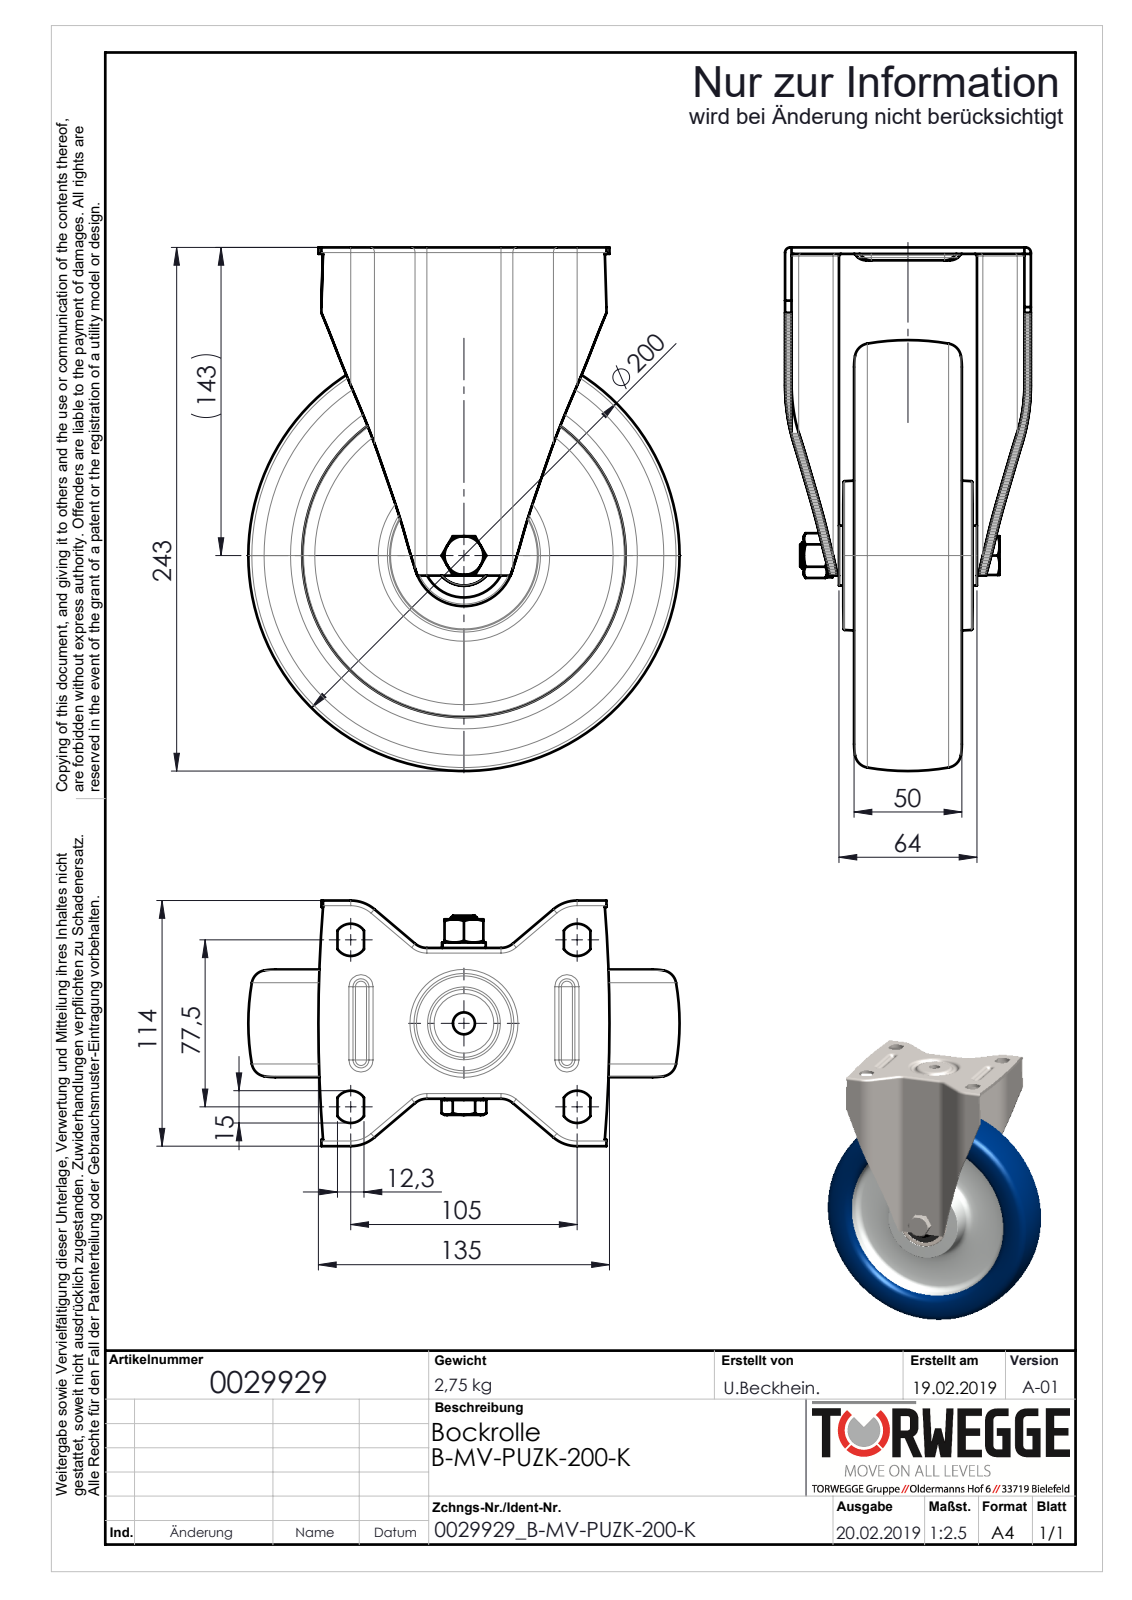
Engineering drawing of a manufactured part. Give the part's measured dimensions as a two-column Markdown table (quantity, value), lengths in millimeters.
| quantity | value |
| --- | --- |
| part name | 0029929_B-MV-PUZK-200-K_(A-01) |
| STEP written by | SolidWorks 2018 (AUTOMOTIVE_DESIGN) |
| units | millimeters |
| bodies | 10 solids, 1224 faces (883 planar, 145 cylindrical, 196 other) |
| overall size | 241.37 × 200 × 114 |
| volume | 1 152 000 mm³ |
| surface area | 239 561 mm² |
| round holes (diameter × count) | 10.2 × 2, 12 × 1, 12.2 × 1, 12.4 × 1, 12.5 × 1, 20 × 1, 20.5 × 1, 35 × 1, 38.9 × 1 |
| round bosses / shafts (diameter × count) | 47 × 1, 28.1 × 1, 27.8 × 1, 24 × 1, 20.2 × 1, 19.6 × 1, 18 × 1 |
| partial cylindrical surfaces (radius × count) | 1 × 12, 2.4 × 8, 4 × 8, 3 × 6, 7.5 × 4, 8.5 × 4, 11.5 × 4, 14 × 4 |
| main face-to-face distances | 3, 24.13, 62.5, 27.13, 21.13, 59.5, 24.25, 86.75, 65.5, 46 |
